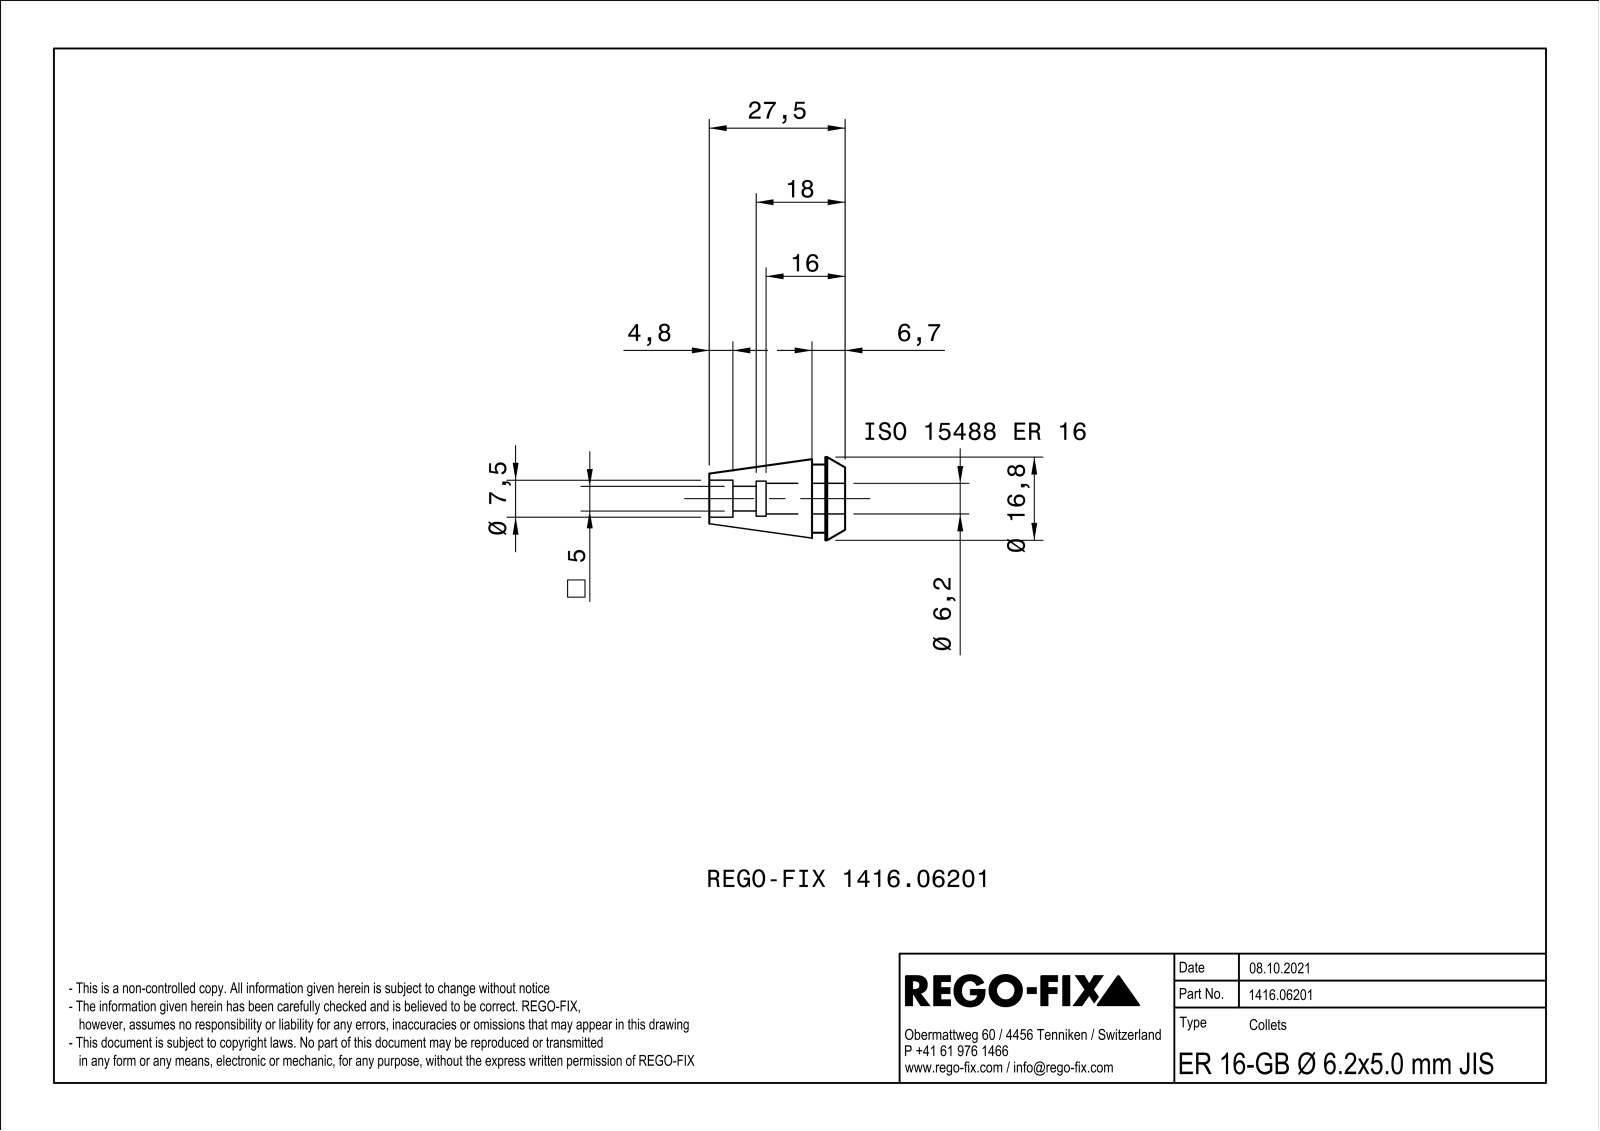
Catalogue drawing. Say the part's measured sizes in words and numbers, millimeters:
The part is named "NOCUT". Its 3-D file was written by "SIEMENS PLM Software Solid Edge ST10 (AUTOMOTIVE_DESIGN)". It is 1 solid with 164 faces: 64 planar, 40 cylindrical and 60 other. Overall it measures 27.5 by 16.8 by 16.8 millimeters. Its volume is 2 628 cubic millimeters and its surface area 3 115 square millimeters. Round holes: 1 of diameter 6.2, 1 of diameter 7.5. Round bosses or shafts: 1 of diameter 16.8, 1 of diameter 13.8. Partial cylindrical surfaces (rounded edges, fillets, slot ends): 1 of radius 2.85, 1 of radius 3.4, 1 of radius 3.55. The main face-to-face distances are 0.6, 4, 6.7, 2.7, 2.4, 3, 27.5, 23.5, 20.8, 5.4.
